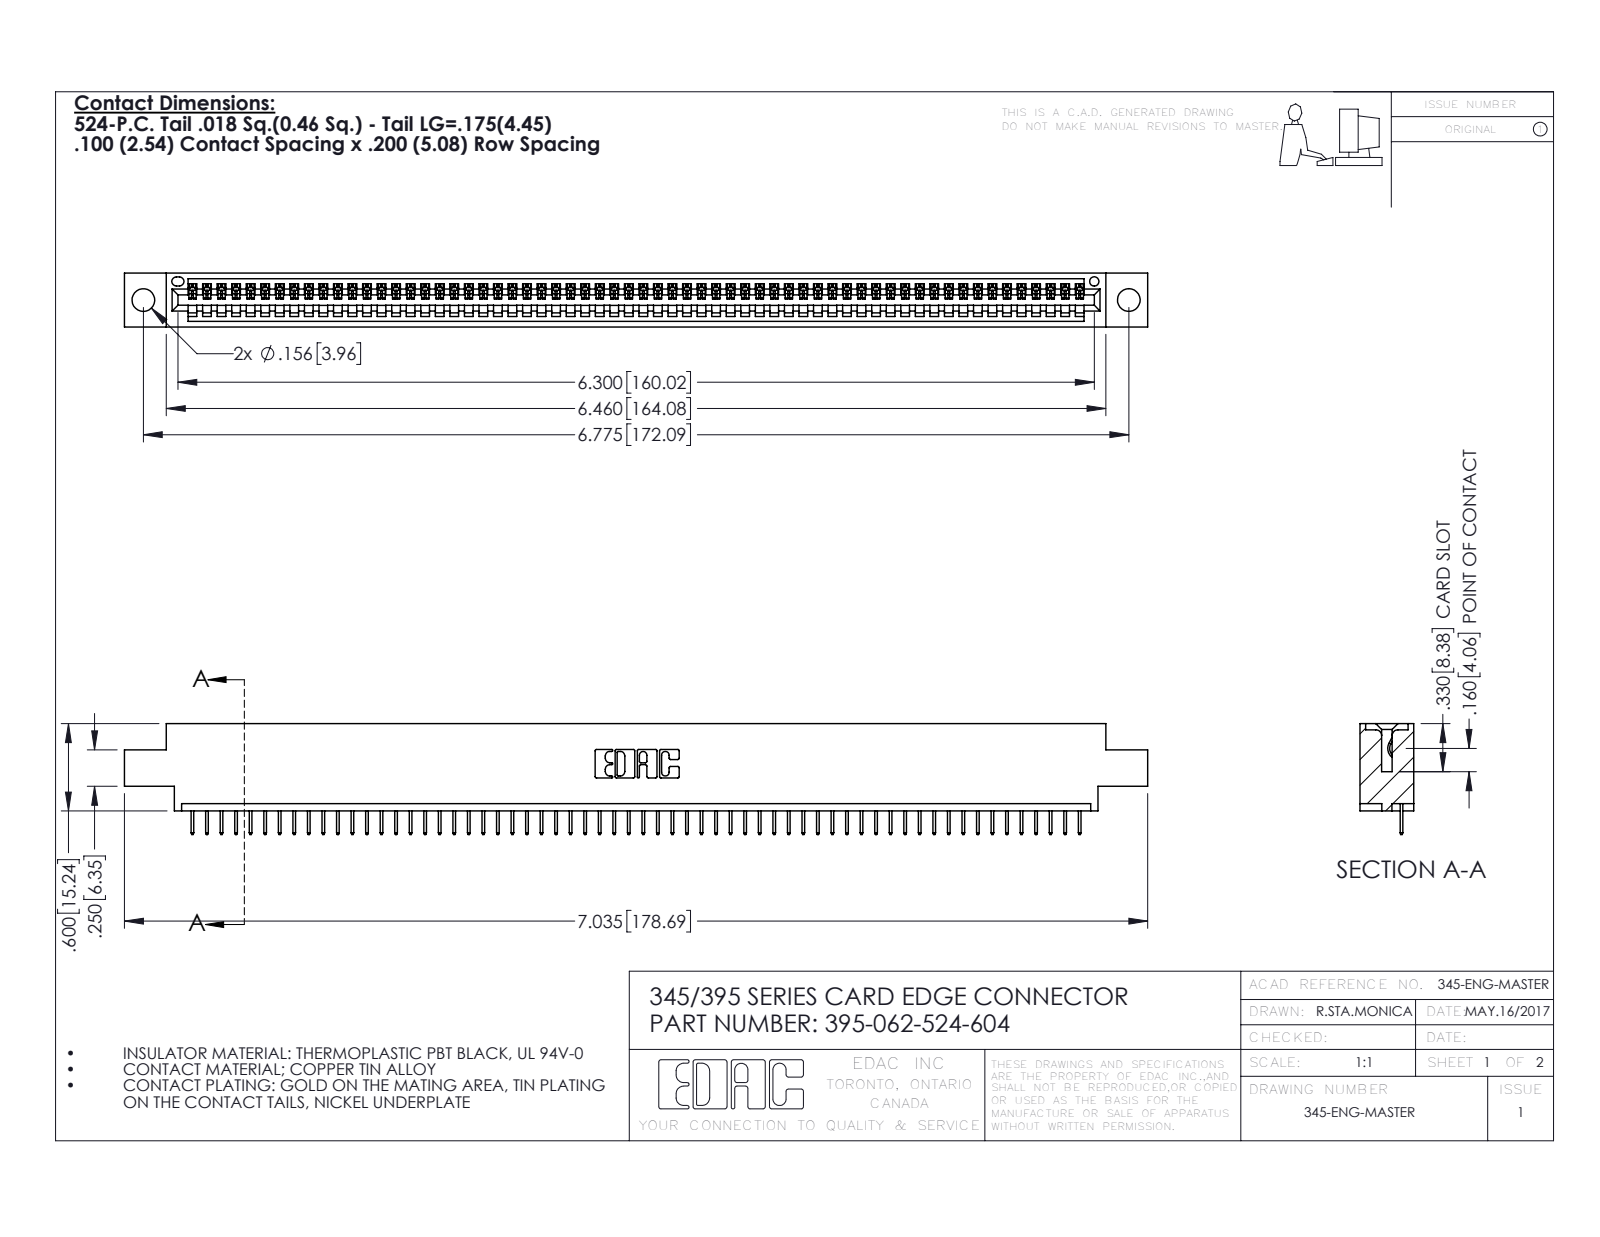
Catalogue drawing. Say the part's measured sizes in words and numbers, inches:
The part is named "345-292-001_345-293-124; 345 Part_0.170 Offset - 0.156 Dia-TH; 395-062-524-604". Its 3-D file was written by "SolidWorks 2016 (CONFIG_CONTROL_DESIGN)". It is 63 solids with 3974 faces: 2936 planar, 1038 cylindrical and 0 other. Overall it measures 7.035 by 0.762 by 0.37 inches. Its volume is 1.018 cubic inches and its surface area 33.49 square inches. Round holes: 2 of diameter 0.156, 1 of diameter 0.064. Partial cylindrical surfaces (rounded edges, fillets, slot ends): 124 of radius 0.006, 22 of radius 0.01, 6 of radius 0.007, 6 of radius 0.031, 3 of radius 0.026, 2 of radius 0.031, 2 of radius 0.04, 1 of radius 0.014. The main face-to-face distances are 0.072, 0.298, 0.37, 0.2, 0.098, 0.272, 0.025, 0.225, 0.072, 0.175. The hole center spacings are 0.27, 6.539, 6.775.
